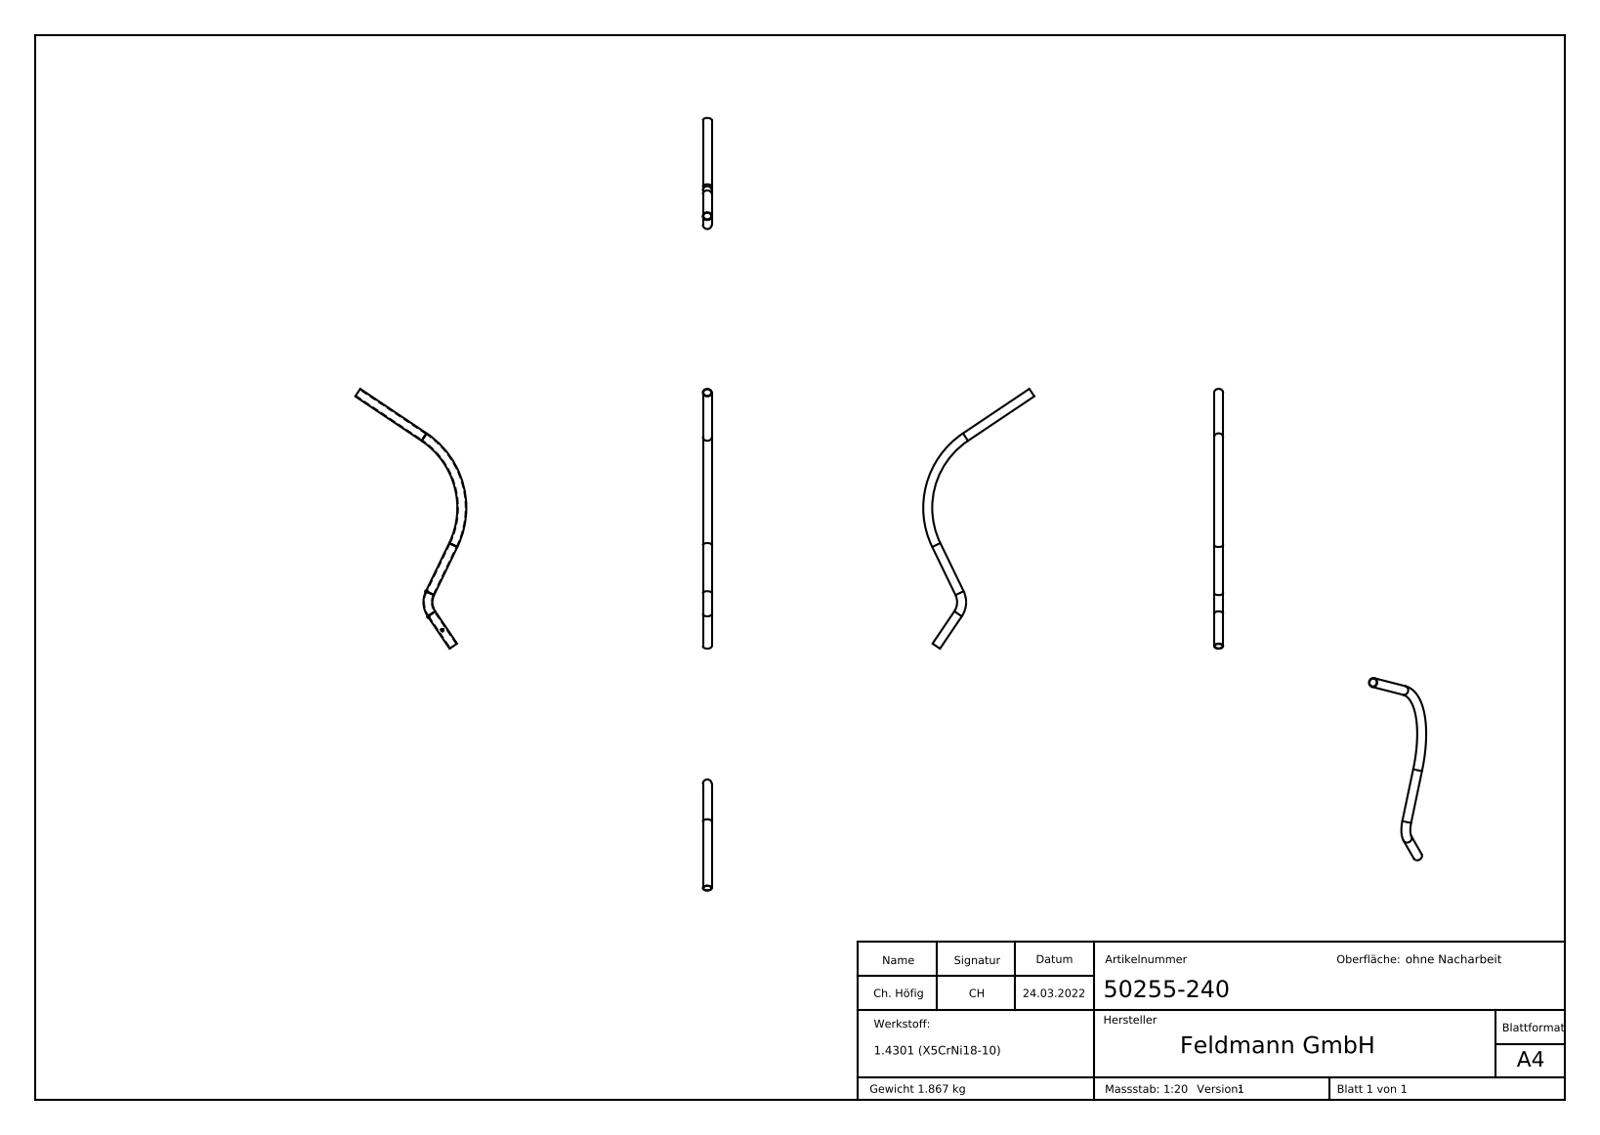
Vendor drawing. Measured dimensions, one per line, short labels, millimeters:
name: 50255-240
written by: SolidWorks 2018 (CONFIG_CONTROL_DESIGN)
unit: mm
bodies: 1 solid, 283 faces (103 planar, 30 cylindrical, 150 other)
size: 975.17 × 416.95 × 33.7
volume: 236 273 mm³; area: 236 685 mm²
holes: 3× ⌀29.7
bosses: 3× ⌀33.7
rounds: 1× R14.95
face distances: 2.97, 0.41, 1.12, 0.54, 2.03, 4.22, 1, 4.09, 3.26, 0.72
